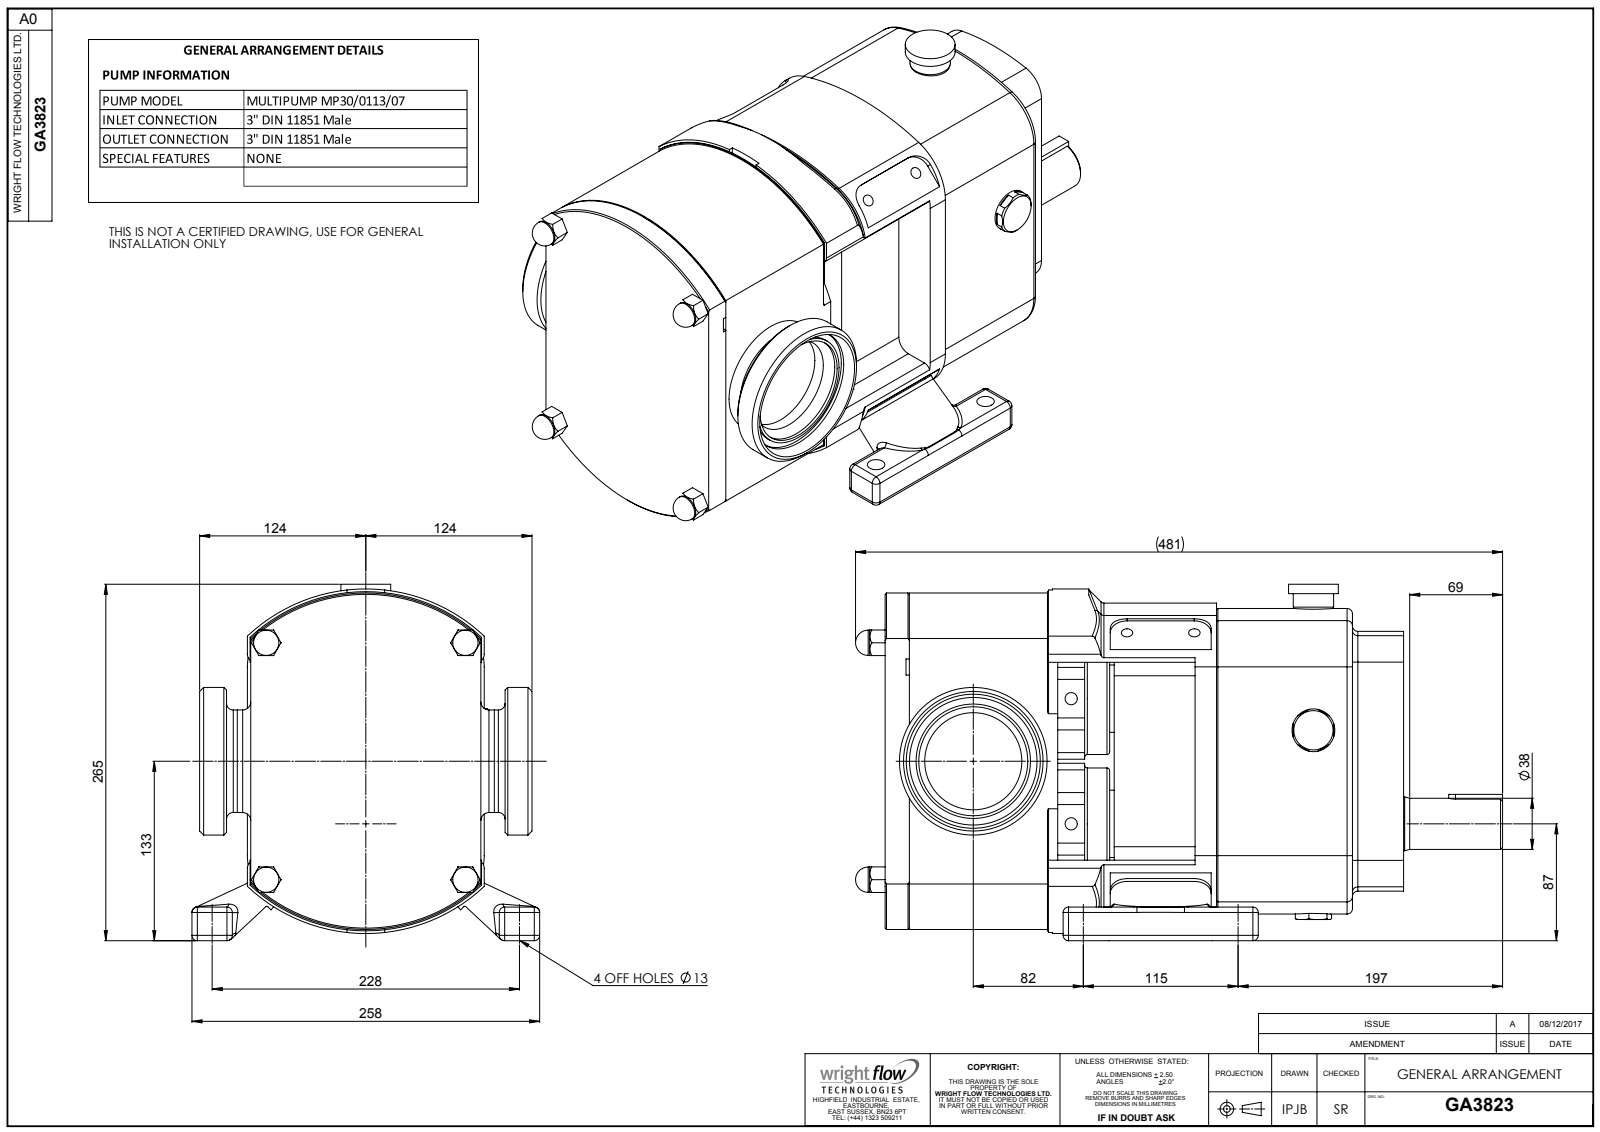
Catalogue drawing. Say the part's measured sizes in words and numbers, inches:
The part is named "GA3823; Copy of CP30-0113-07 H B^GA3823; Copy of Z94-5031-55 - 3 INCH DIN11851^GA3823". Its 3-D file was written by "SolidWorks 2023 (AUTOMOTIVE_DESIGN)". It is 3 solids with 737 faces: 269 planar, 249 cylindrical and 219 other. Overall it measures 18.93 by 10.427 by 10.172 inches. Its volume is 793.9 cubic inches and its surface area 897.7 square inches. Round holes: 4 of diameter 0.335, 4 of diameter 0.398, 4 of diameter 0.512, 2 of diameter 0.358, 1 of diameter 1.378, 1 of diameter 2.843, 1 of diameter 3.189, 1 of diameter 3.732. Round bosses or shafts: 4 of diameter 0.74, 2 of diameter 3.268, 2 of diameter 1.969, 1 of diameter 4.319, 1 of diameter 3.346, 1 of diameter 3, 1 of diameter 2.996, 1 of diameter 1.575. Partial cylindrical surfaces (rounded edges, fillets, slot ends): 44 of radius 0.157, 16 of radius 0.039, 12 of radius 0.394, 10 of radius 0.236, 4 of radius 0.492, 4 of radius 0.495, 4 of radius 0.496, 4 of radius 0.787. The main face-to-face distances are 0.059, 6.673, 5.472, 1.496, 6.702, 8.467, 15.169, 6.732, 1.201, 5.531. The hole center spacings are 2.506, 1.97, 3.399, 3.543, 4.528, 5.007, 8.095, 8.991.
